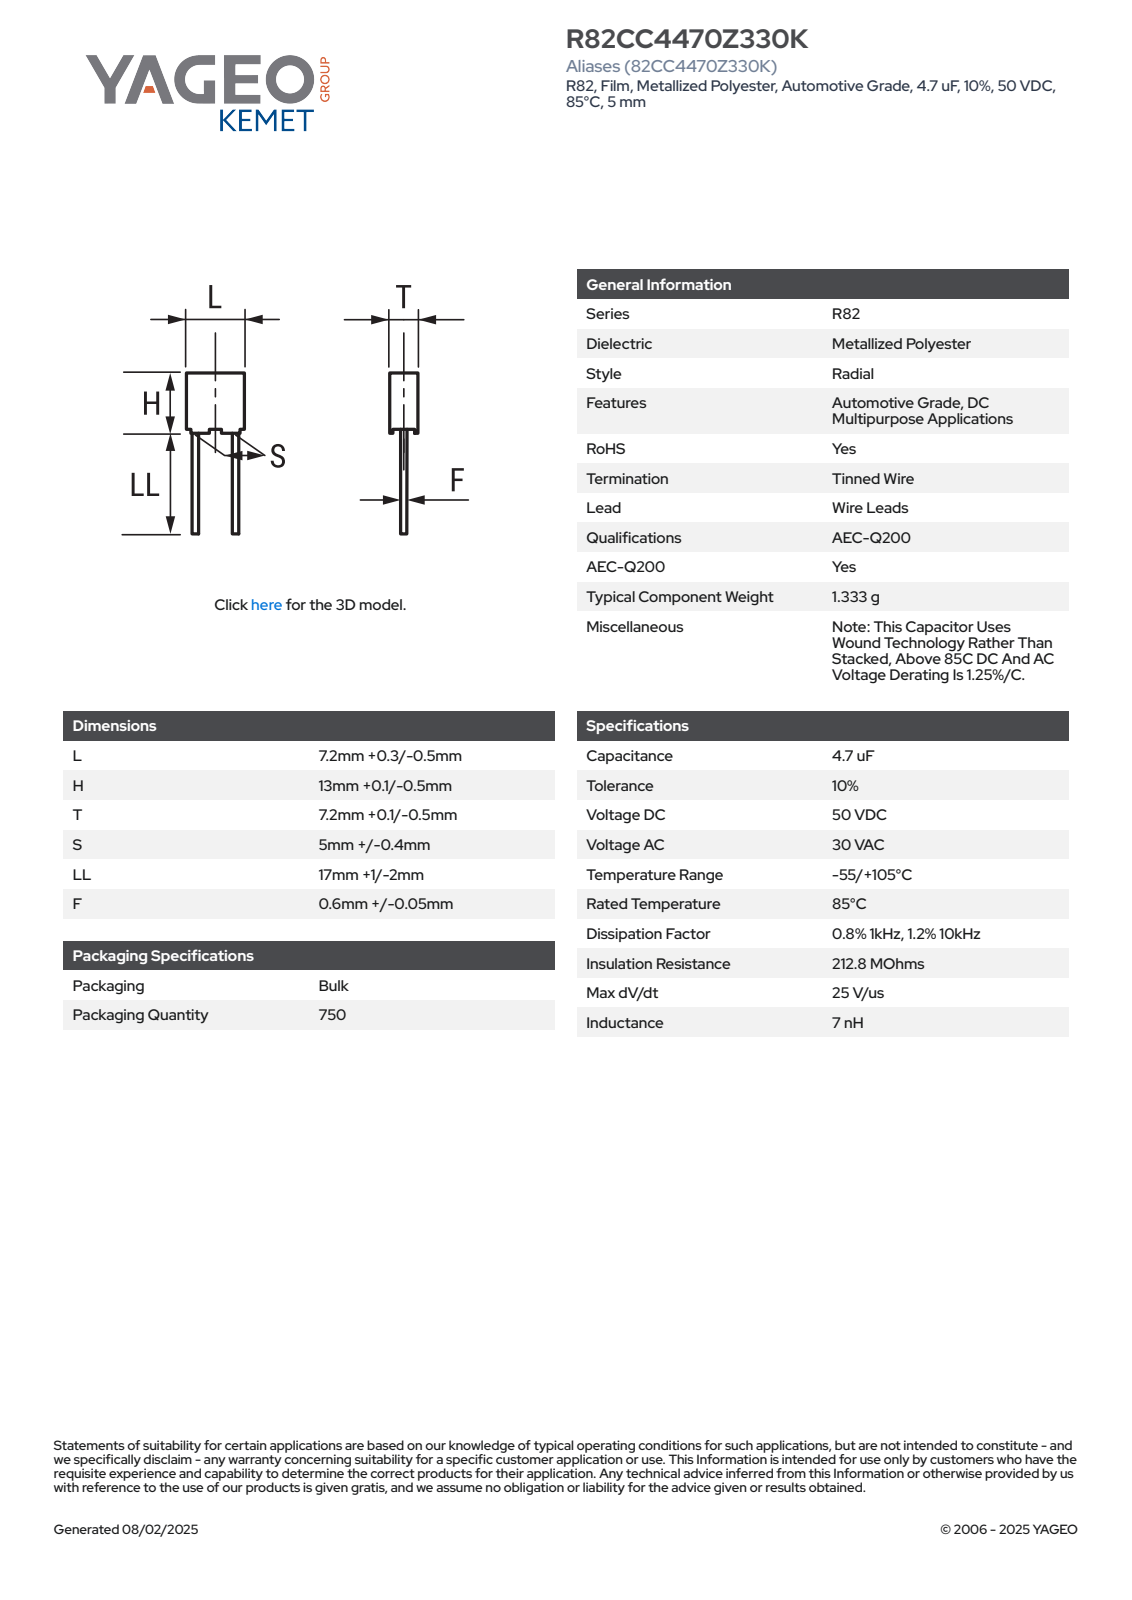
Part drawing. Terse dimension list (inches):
name: CFR_RB3_7.2X13X7.2_L7.5H13.1T7.3S5LL18F0.65
written by: SolidWorks 2014 (AUTOMOTIVE_DESIGN)
unit: in
bodies: 4 solids, 85 faces (77 planar, 8 cylindrical, 0 other)
size: 1.224 × 0.295 × 0.287
volume: 0.042 in³; area: 0.913 in²
bosses: 2× ⌀0.026
rounds: 4× R0.02
face distances: 0.287, 0.295, 0.486, 0.285, 0.278, 0.03, 0.516, 0.276, 0.268, 0.018
